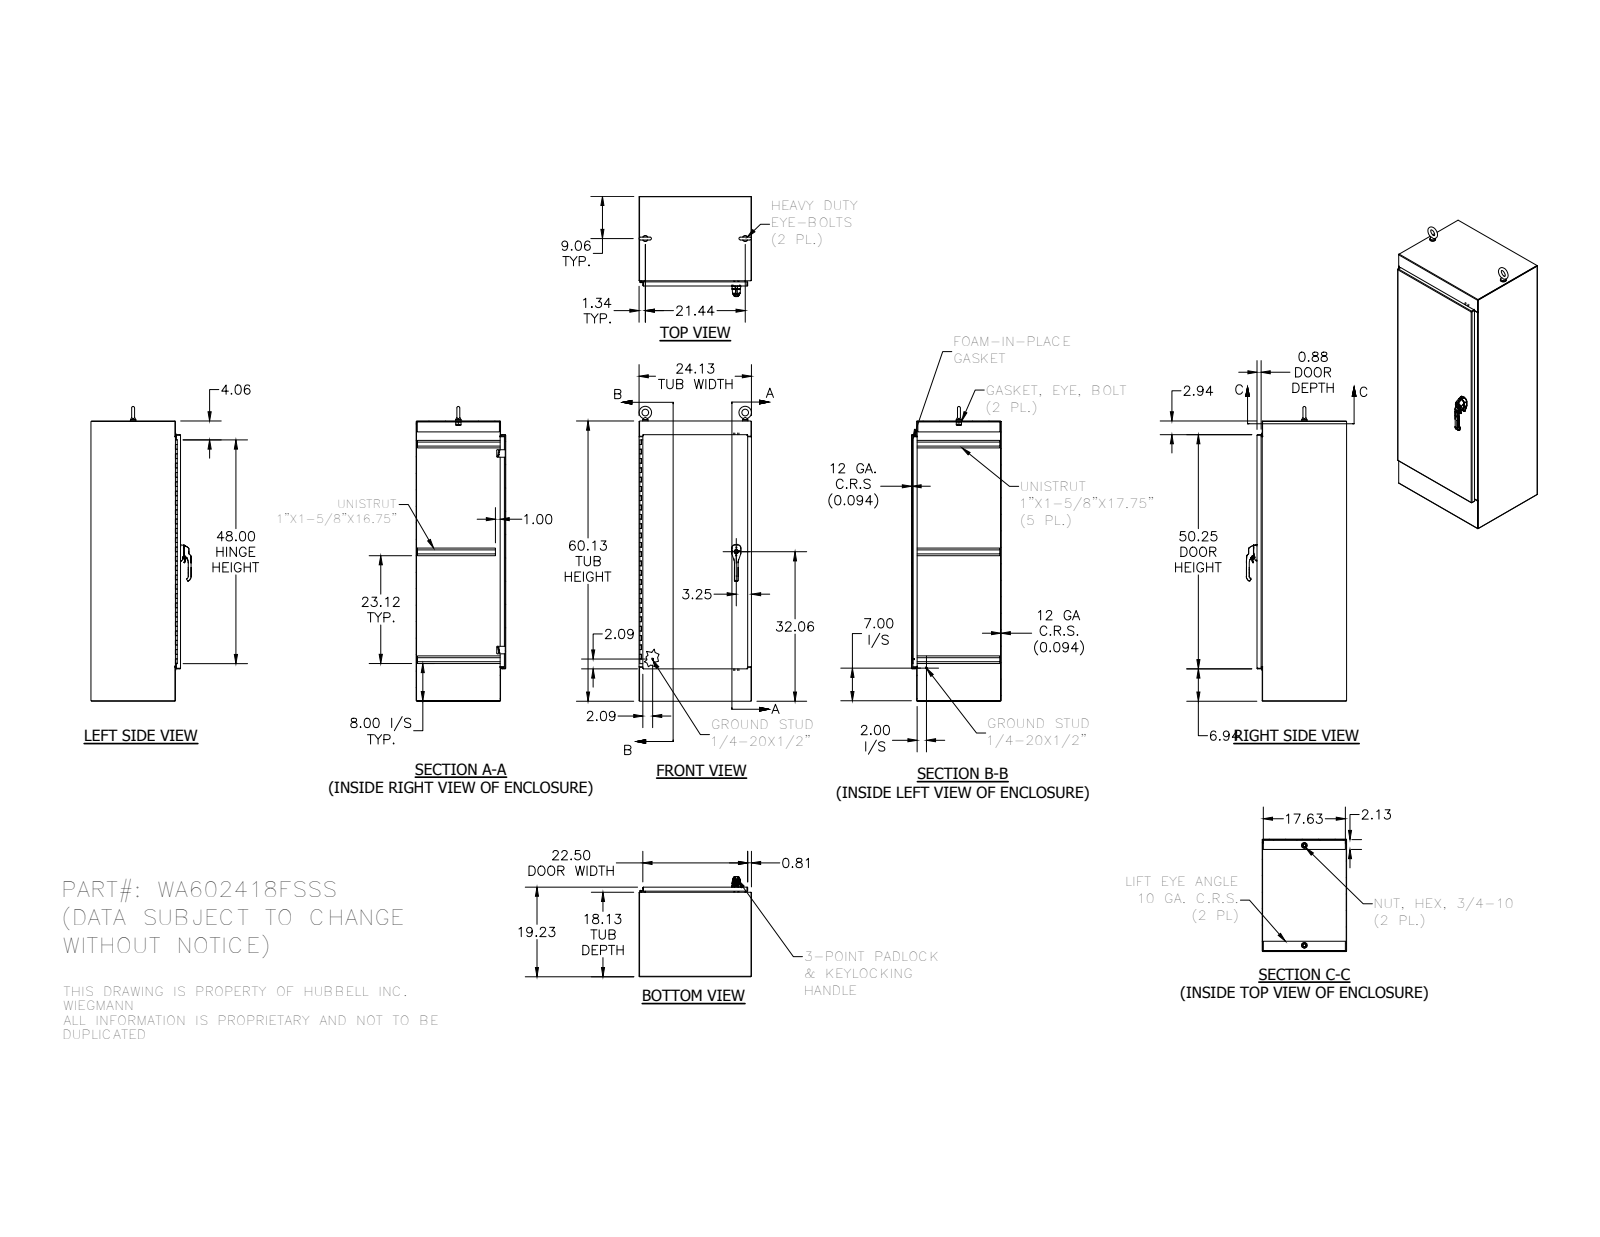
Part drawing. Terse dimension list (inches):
name: WA602418FSBLR; WA2418FSTOP; WA2418FSBTM; WA6024FSDR (+8 more)
written by: Autodesk Inventor 2014 (AUTOMOTIVE_DESIGN)
unit: in
bodies: 46 solids, 2665 faces (1084 planar, 934 cylindrical, 647 other)
size: 63.248 × 24.125 × 21.476
volume: 675.5 in³; area: 14 210 in²
holes: 8× ⌀0.276, 8× ⌀0.375, 4× ⌀0.2, 3× ⌀0.213, 3× ⌀0.28, 2× ⌀0.315, 2× ⌀0.402, 2× ⌀0.407, 2× ⌀0.413, 2× ⌀0.642, 2× ⌀0.813, 1× ⌀0.122
bosses: 2× ⌀1.25, 2× ⌀1.12, 2× ⌀0.75, 2× ⌀0.531, 2× ⌀0.526, 2× ⌀0.435, 2× ⌀0.337, 2× ⌀0.25
rounds: 178× R0.02, 101× R0.012, 23× R0.019, 16× R0.01, 16× R0.031, 16× R0.125, 14× R0.053, 14× R0.079
face distances: 0.094, 19.133, 24.031, 23.938, 19.039, 19.227, 24.125, 60.031, 18.031, 1.102
hole spacings: 5.333, 16, 10.667, 21.333, 42.571, 0.38, 0.382, 0.382
